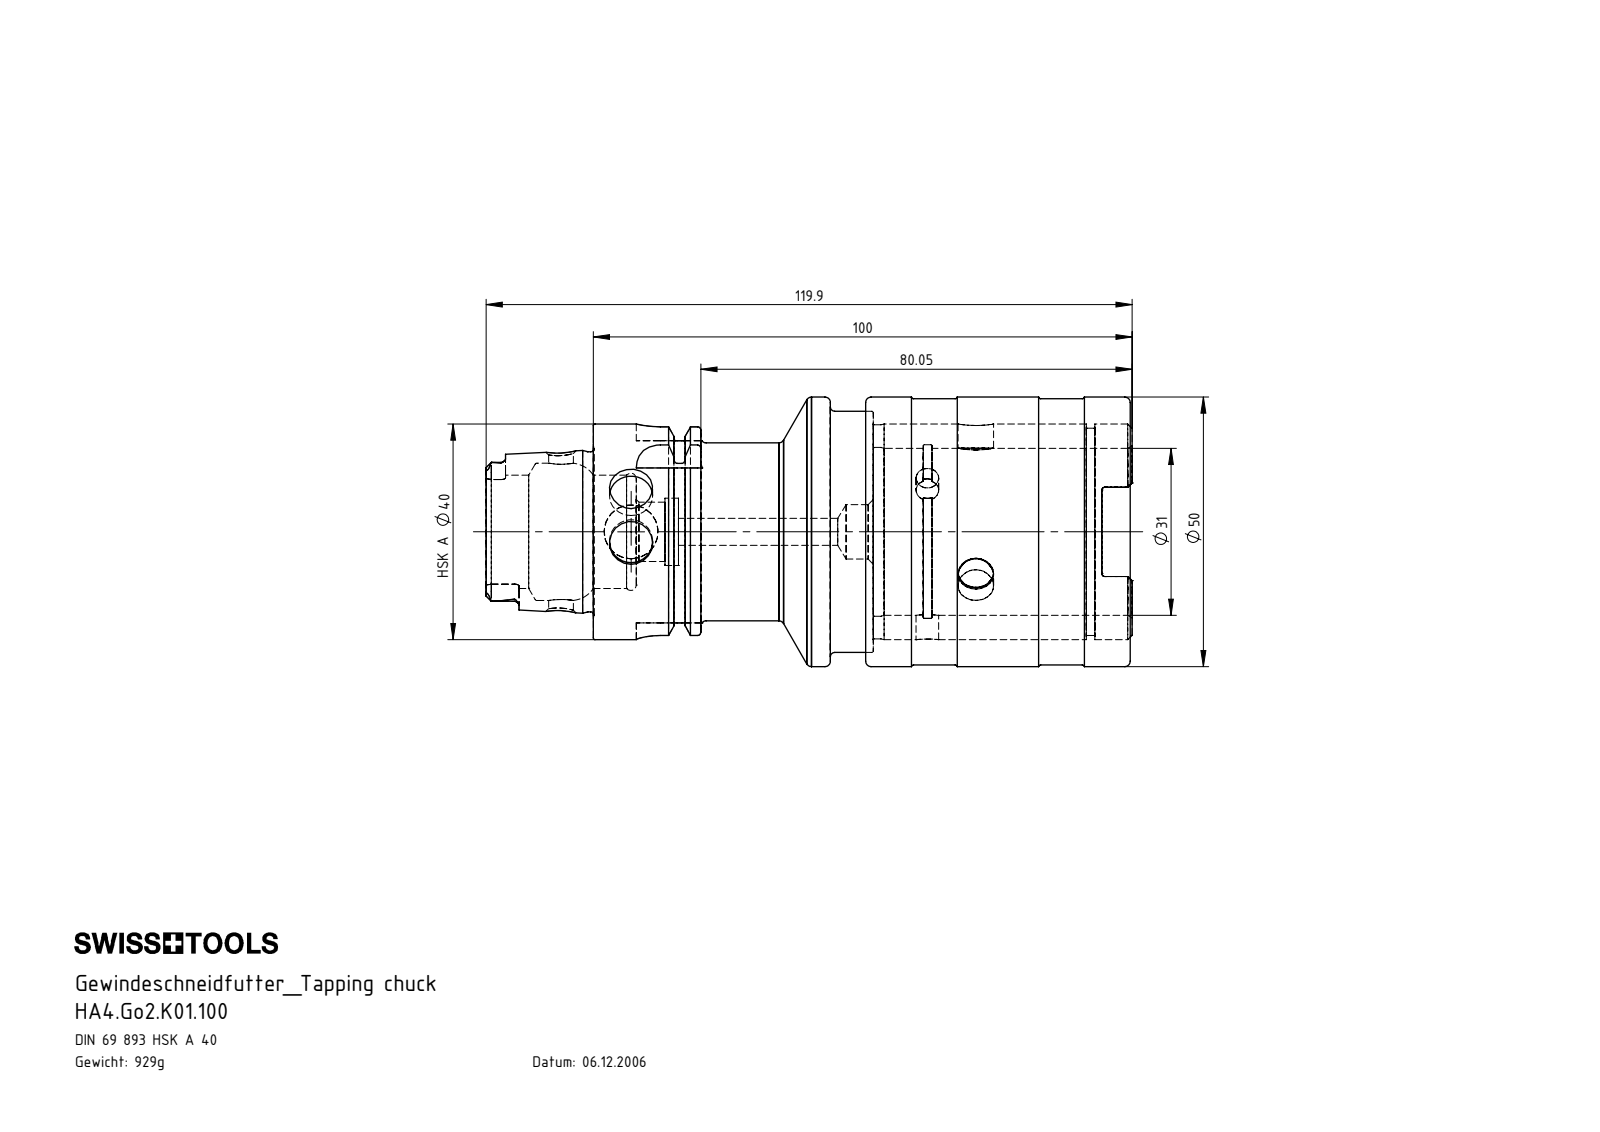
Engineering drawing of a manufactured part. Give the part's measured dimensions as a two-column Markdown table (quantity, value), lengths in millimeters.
| quantity | value |
| --- | --- |
| part name | Boden Go2; Federring aussen Go2_gespannt; HA4-Go2.K01.100_B_Fertigbearbeitung; Feder klein Go2_gespannt (+6 more) |
| STEP written by | SolidWorks 2017 (CONFIG_CONTROL_DESIGN) |
| units | millimeters |
| bodies | 10 solids, 392 faces (90 planar, 124 cylindrical, 178 other) |
| overall size | 119.9 × 50 × 50 |
| volume | 118 218 mm³ |
| surface area | 50 123 mm² |
| round holes (diameter × count) | 4.2 × 3, 6.6 × 3, 8 × 2, 2.5 × 1, 4.6 × 1, 5 × 1, 10 × 1, 10.1 × 1, 11 × 1, 12.5 × 1, 21 × 1, 25.5 × 1 |
| round bosses / shafts (diameter × count) | 50 × 1, 49.4 × 1, 44.75 × 1, 40 × 1, 39.7 × 1, 38.45 × 1, 34.75 × 1, 33 × 1 |
| partial cylindrical surfaces (radius × count) | 0.9 × 6, 1.88 × 4, 4.5 × 4, 3.1 × 3, 0.5 × 2 |
| main face-to-face distances | 12, 12.65, 0.65, 0.7, 12.7, 14.6, 14.55, 13.9, 1.9, 10.2 |
| hole center spacings | 9, 68, 77 |
